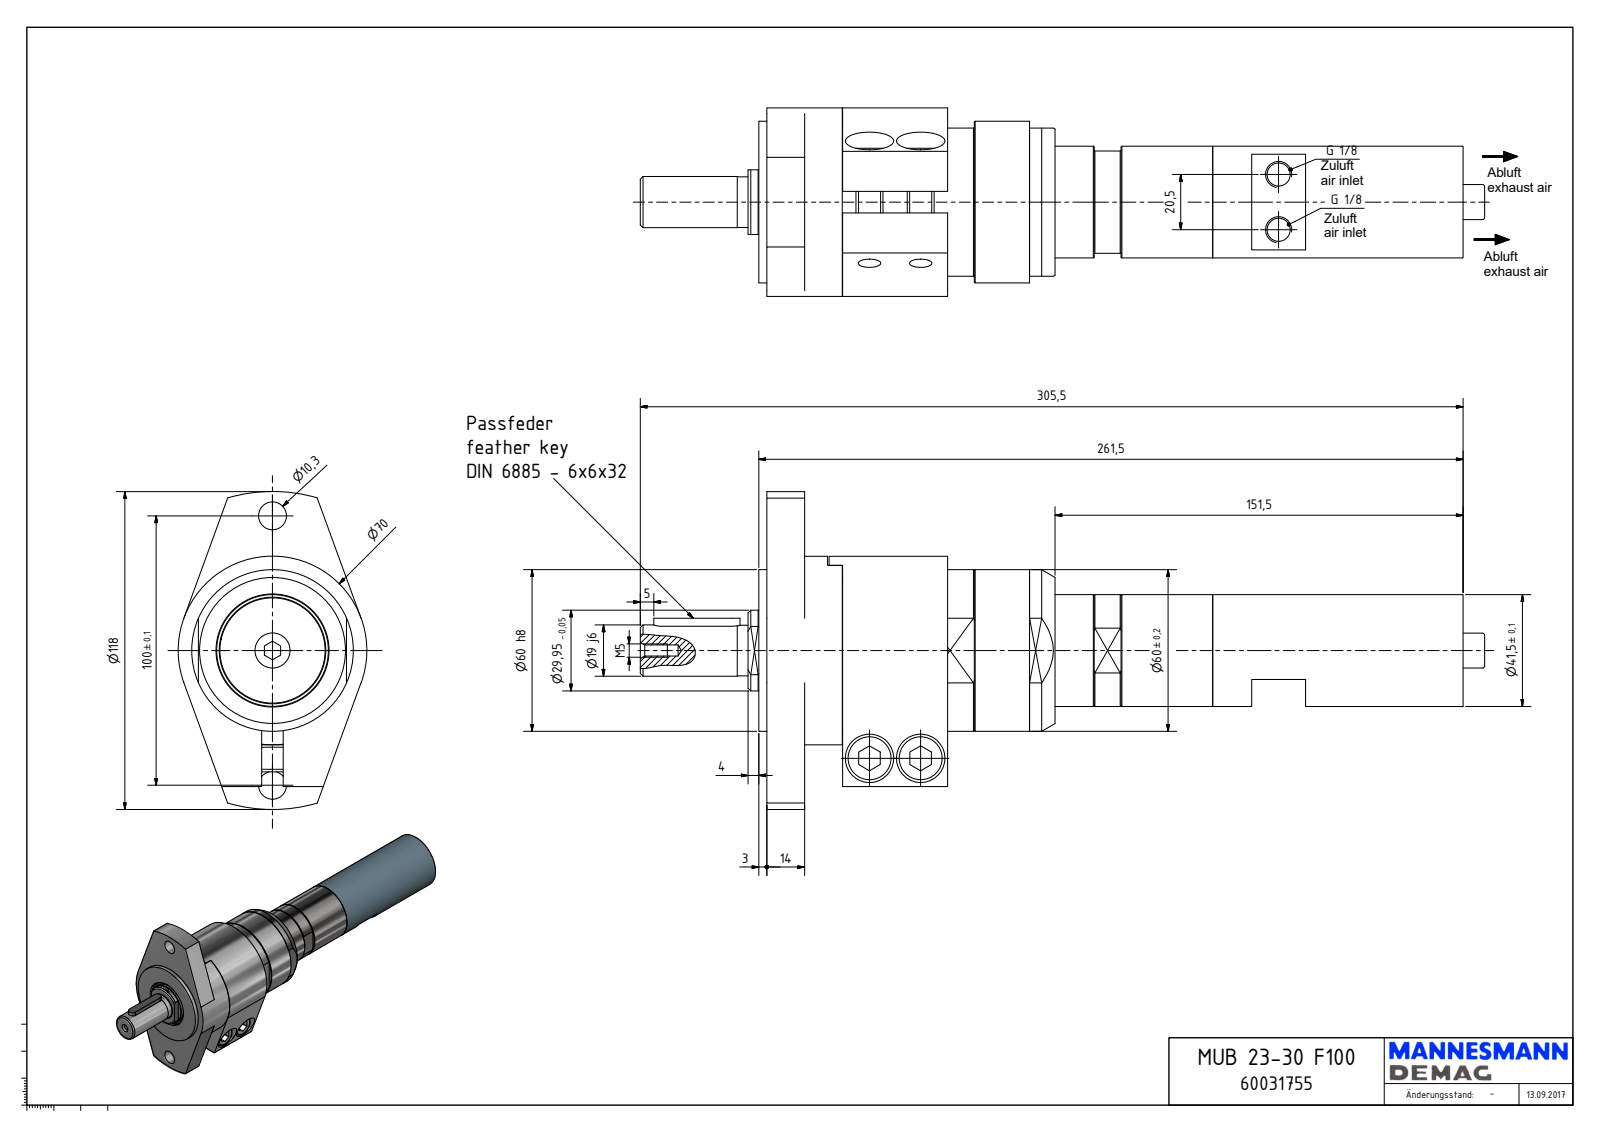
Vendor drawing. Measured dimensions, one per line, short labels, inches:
name: MUB 23-25 F100_60031755
written by: Autodesk Inventor 2018 (AUTOMOTIVE_DESIGN)
unit: in
bodies: 1 solid, 241 faces (117 planar, 83 cylindrical, 41 other)
size: 12.343 × 4.646 × 2.756
volume: 39.22 in³; area: 123.5 in²
holes: 2× ⌀0.33, 2× ⌀0.337, 2× ⌀0.406, 2× ⌀0.413, 2× ⌀0.709, 1× ⌀0.061, 1× ⌀0.157, 1× ⌀0.163, 1× ⌀0.217, 1× ⌀0.335, 1× ⌀1.378, 1× ⌀1.555
bosses: 2× ⌀0.63, 2× ⌀0.394, 1× ⌀2.756, 1× ⌀2.362, 1× ⌀2.172, 1× ⌀1.634, 1× ⌀1.535, 1× ⌀1.417
rounds: 2× R0.039, 2× R0.063, 2× R0.079, 2× R0.098, 2× R0.118, 1× R0.315, 1× R0.319, 1× R0.527
face distances: 0.551, 0.669, 0.118, 2.76, 1.535, 2.642, 2.091, 1.224, 1.106, 0.555
hole spacings: 1.969, 4.996, 0.748, 0.807, 3.937
